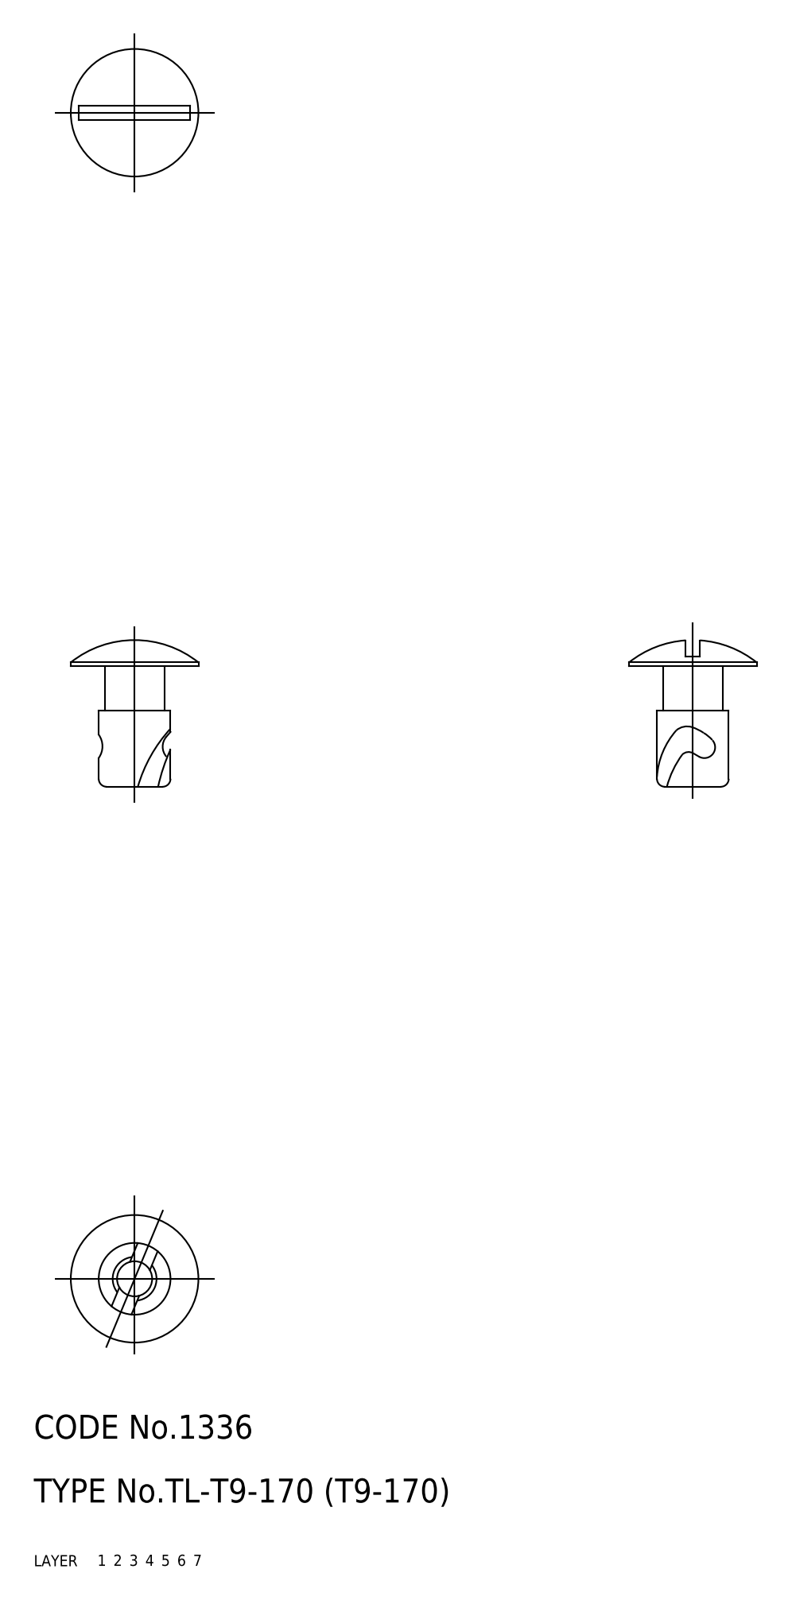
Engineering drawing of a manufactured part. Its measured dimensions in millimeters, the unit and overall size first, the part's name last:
Units: millimetres
Overall size (bounding box): 18.37 × 16 × 16
Volume: 954 mm³
Bodies: 1 solid, 35 faces (0 planar, 0 cylindrical, 35 other)
Part name (STEP PRODUCT): 67113775
STEP written by: CADfix (AUTOMOTIVE_DESIGN)
